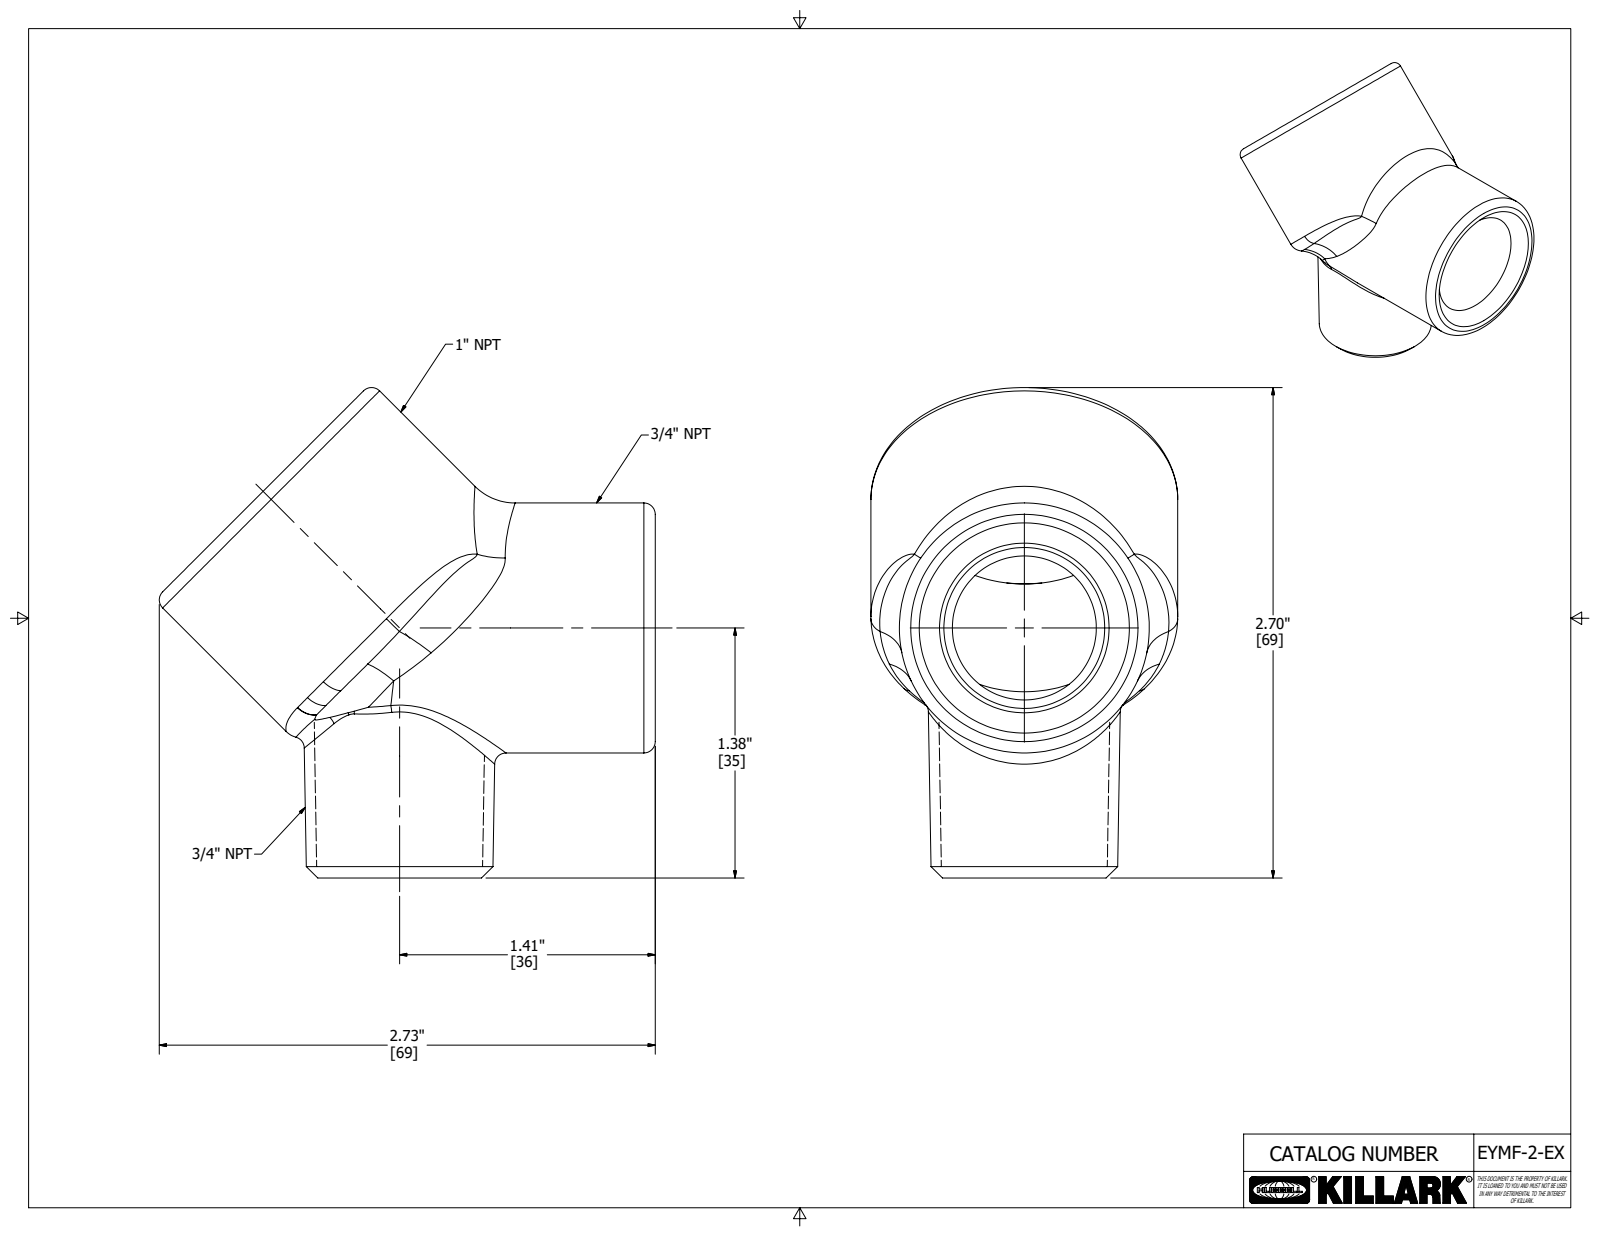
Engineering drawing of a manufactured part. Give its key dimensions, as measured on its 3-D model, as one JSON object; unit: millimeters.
{"part_name": "12692-2", "step_written_by": "Autodesk Inventor 2020 (AUTOMOTIVE_DESIGN)", "units": "millimeters", "bodies": {"solids": 1, "faces": 110, "planar": 14, "cylindrical": 15, "other": 81}, "overall_size": [73.9, 71.6, 42.9], "volume_mm3": 43470, "surface_area_mm2": 17710, "round_holes": [[24.4, 1], [30, 1], [30.8, 1]], "round_bosses_or_shafts": [[42.8, 1], [34.9, 1], [27.3, 1]], "partial_cylinders_radius": [[0.8, 2], [0.3, 1], [10.1, 1], [10.8, 1], [19.1, 1]], "face_to_face_distances": [36.5, 22.2, 4, 26.2, 28.6, 8, 20.7, 26.9, 6.2]}
